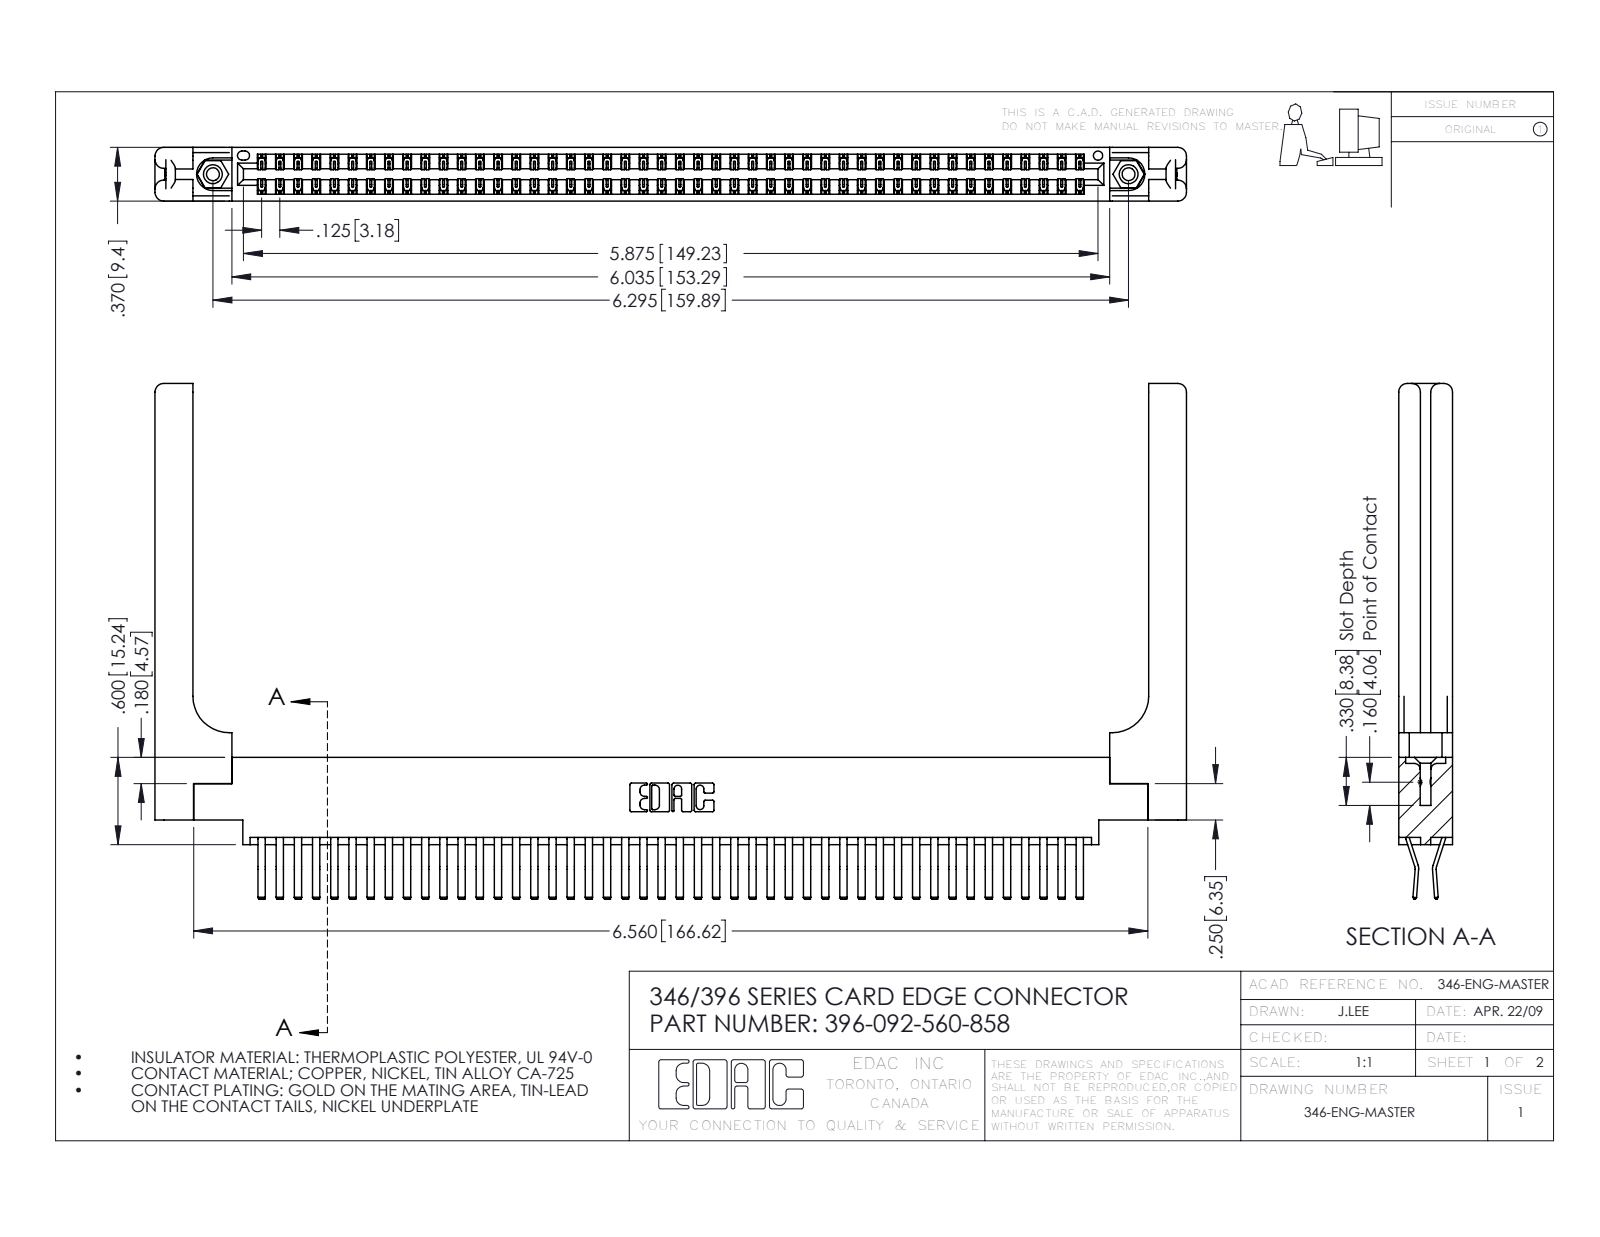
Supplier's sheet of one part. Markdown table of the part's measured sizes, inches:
| quantity | value |
| --- | --- |
| part name | 345-292-001_560 Tail; 345-250-001_345-250-001-102; 346-220-058_345-220-058; 396-092-560-858 (+1 more) |
| STEP written by | SolidWorks 2016 (CONFIG_CONTROL_DESIGN) |
| units | inches |
| bodies | 97 solids, 5350 faces (3448 planar, 1842 cylindrical, 60 other) |
| overall size | 7.091 × 3.545 × 0.37 |
| volume | 1.558 in³ |
| surface area | 49.02 in² |
| round holes (diameter × count) | 0.089 × 2, 0.125 × 2, 0.156 × 2, 0.064 × 1 |
| round bosses / shafts (diameter × count) | 0.155 × 2 |
| partial cylindrical surfaces (radius × count) | 0.006 × 138, 0.01 × 22, 0.06 × 16, 0.007 × 6, 0.031 × 6, 0.026 × 3, 0.01 × 2, 0.014 × 2 |
| main face-to-face distances | 0.37, 0.048, 0.322, 0.072, 0.025, 0.148, 0.15, 0.25, 0.298, 0.275 |
| hole center spacings | 0.246, 6.086, 6.295 |
